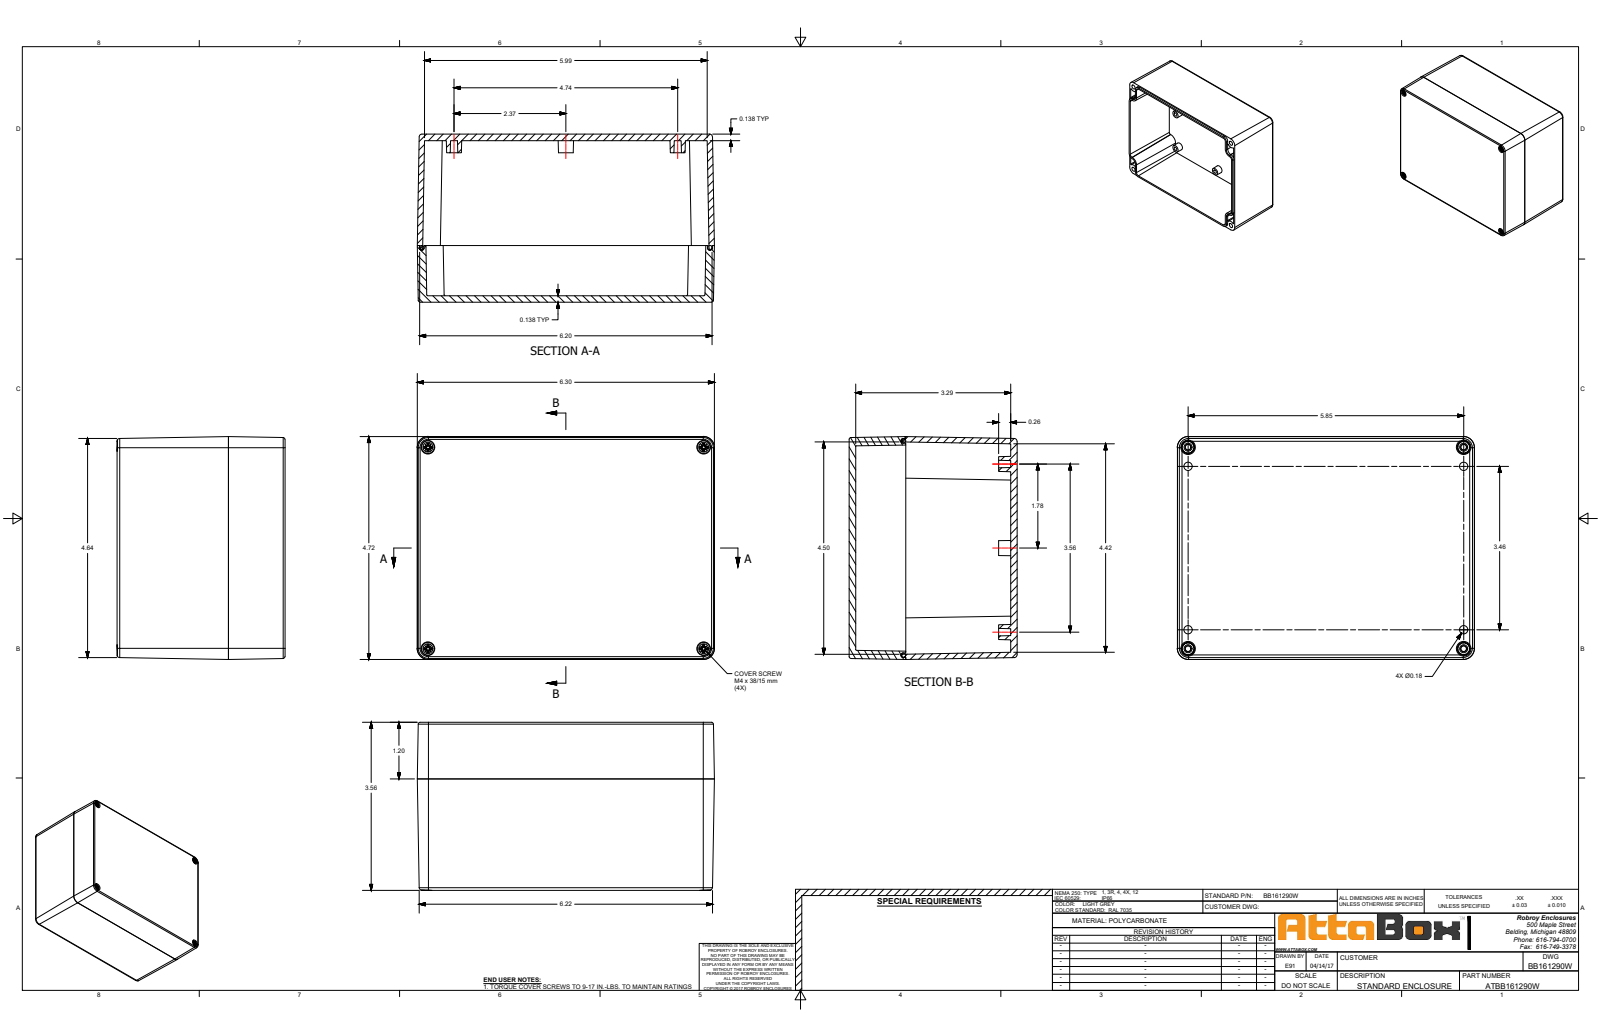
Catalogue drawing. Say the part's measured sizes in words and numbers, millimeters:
The part is named "BB161290W". Its 3-D file was written by "SolidWorks 2018 (AUTOMOTIVE_DESIGN)". It is 11 solids with 1567 faces: 591 planar, 396 cylindrical and 580 other. Overall it measures 160 by 120 by 90.5 millimeters. Its volume is 306 900 cubic millimeters and its surface area 201 100 square millimeters. Round holes: 8 of diameter 4.5, 4 of diameter 3.3, 4 of diameter 4.8, 4 of diameter 5.1, 4 of diameter 7, 4 of diameter 7.4, 4 of diameter 7.8. Round bosses or shafts: 4 of diameter 6.8, 4 of diameter 4.4, 4 of diameter 4, 4 of diameter 3.3. Partial cylindrical surfaces (rounded edges, fillets, slot ends): 40 of radius 1, 30 of radius 0.5, 12 of radius 4.7, 8 of radius 2.4, 4 of radius 1.5, 4 of radius 2.6, 4 of radius 3.1, 4 of radius 3.6. The main face-to-face distances are 3.5, 87, 2.9, 90.5, 83.5, 120, 117.1, 4.5, 115.5, 112.6. The hole center spacings are 10.3, 98.2, 148.5, 148.8, 178.1, 88, 108.5, 172.6.
